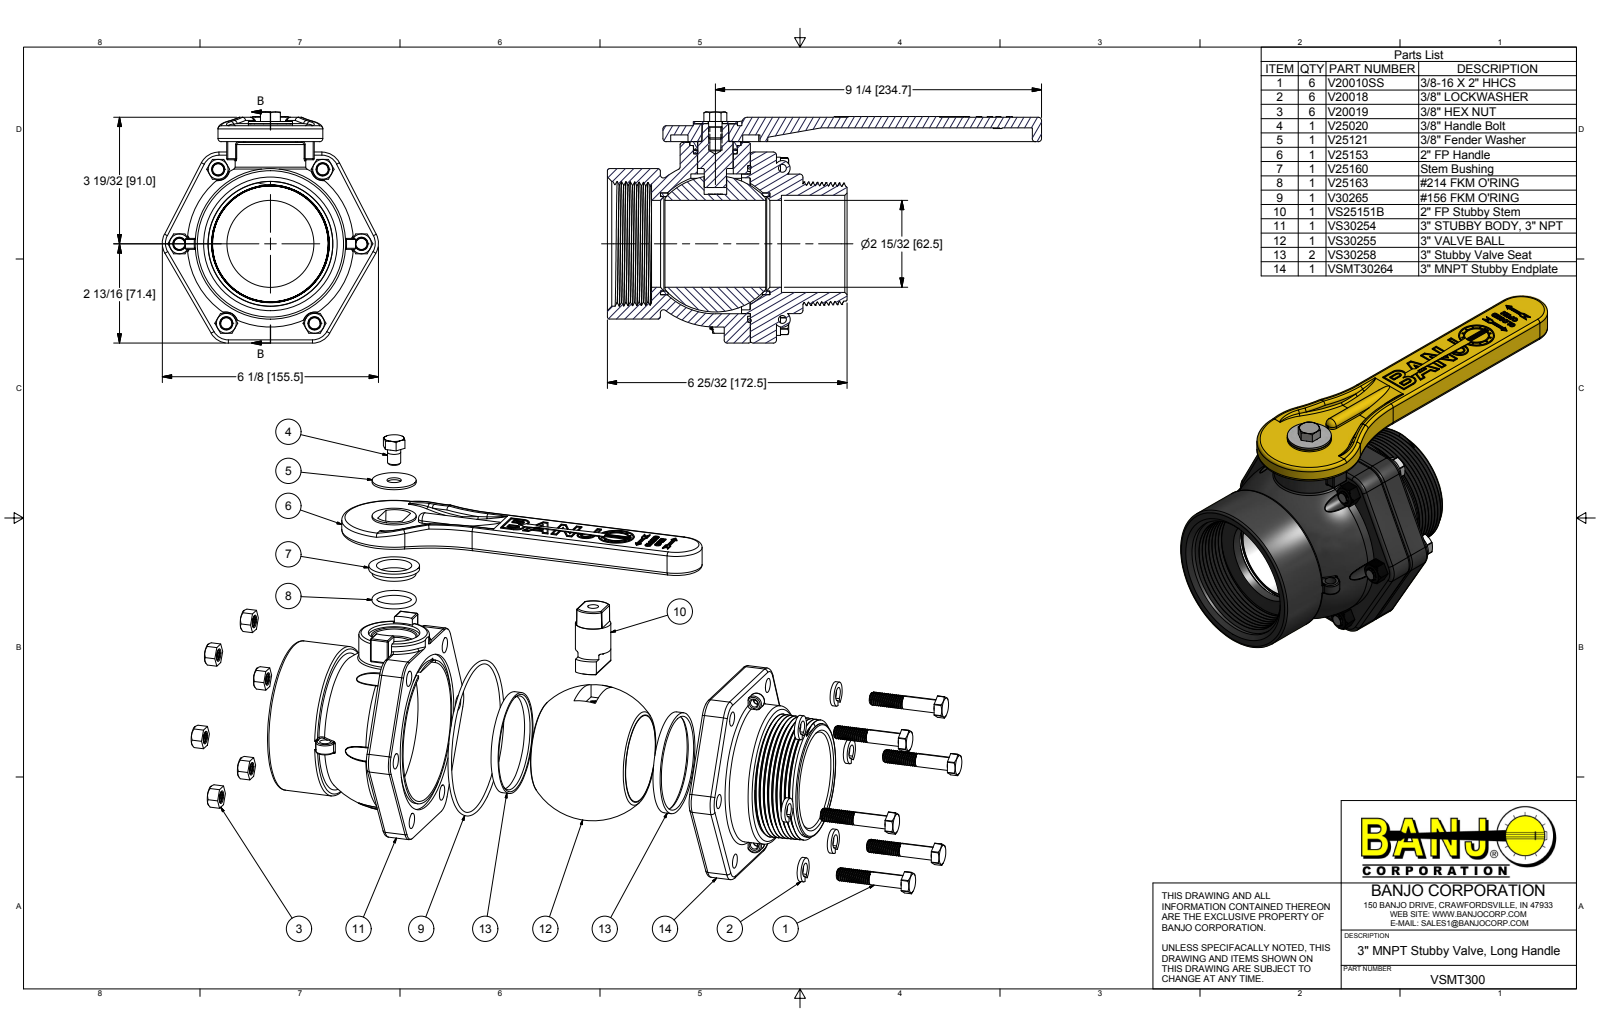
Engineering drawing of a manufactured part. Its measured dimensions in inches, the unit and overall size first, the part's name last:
Units: inches
Overall size (bounding box): 12.3 × 6.543 × 6.124
Round holes (diameter × count): ⌀0.406 ×7, ⌀0.307 ×6, ⌀0.385 ×6, ⌀0.44 ×6, ⌀0.22 ×2, ⌀0.31 ×2, ⌀0.307 ×1, ⌀0.681 ×1, ⌀0.962 ×1, ⌀1 ×1, ⌀1.016 ×1, ⌀1.24 ×1
Round bosses / shafts (diameter × count): ⌀0.324 ×90, ⌀0.375 ×7, ⌀0.687 ×6, ⌀4.26 ×1, ⌀4.098 ×1, ⌀3.95 ×1, ⌀3.945 ×1, ⌀2.969 ×1
Partial cylindrical surfaces — rounded edges, fillets, slot ends (radius × count): R0.03 ×36, R0.09 ×32, R0.162 ×12, R0.032 ×6, R0.315 ×6, R0.32 ×6, R0.56 ×6, R0.563 ×6
Main face-to-face distances: 0.74, 1.48, 0.26, 0.74, 0.3, 0.39, 0.69, 2.8, 0.45, 0.06
Hole centre spacings: 2.38, 2.513, 2.574, 2.577, 2.58, 2.614, 4.366, 4.442
Volume: 75.3 in³ · Surface area: 473.5 in²
Bodies: 30 solids, 2348 faces (629 planar, 799 cylindrical, 920 other)
Part name (STEP PRODUCT): VS30254X; VS30254; V20010SS; V20018 (+8 more)
STEP written by: Autodesk Inventor 2015 (AUTOMOTIVE_DESIGN)
